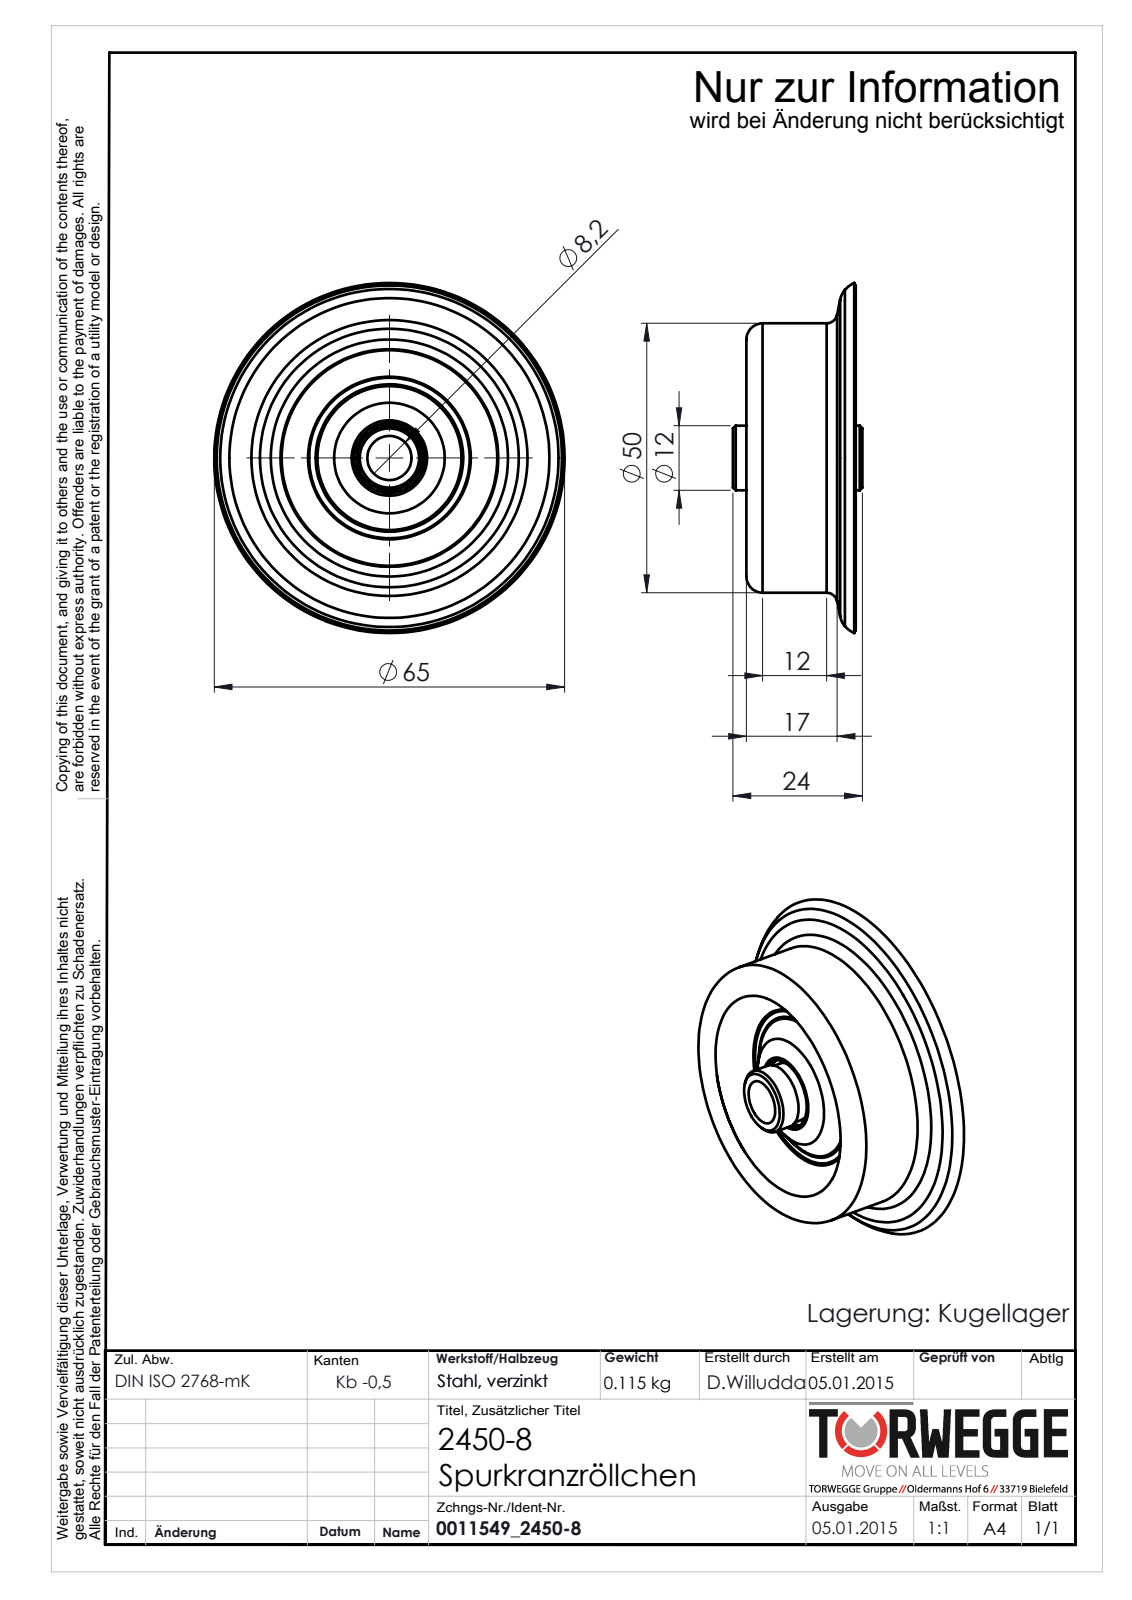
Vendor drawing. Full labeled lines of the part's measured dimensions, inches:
Part name (STEP PRODUCT): 0011549_2450-8
STEP written by: SolidWorks 2014 (AUTOMOTIVE_DESIGN)
Units: inches
Bodies: 6 solids, 171 faces (21 planar, 40 cylindrical, 110 other)
Overall size (bounding box): 2.559 × 2.559 × 0.945
Volume: 0.892 in³ · Surface area: 43.04 in²
Round holes (diameter × count): ⌀0.323 ×1, ⌀0.512 ×1, ⌀0.551 ×1, ⌀1.575 ×1, ⌀1.732 ×1, ⌀1.811 ×1, ⌀1.89 ×1
Round bosses / shafts (diameter × count): ⌀1.969 ×1, ⌀1.181 ×1, ⌀0.472 ×1, ⌀0.441 ×1
Main face-to-face distances: 0.039, 0.157, 0.059, 0.118, 0.217, 0.315, 0.276, 0.197, 0.256, 0.079
